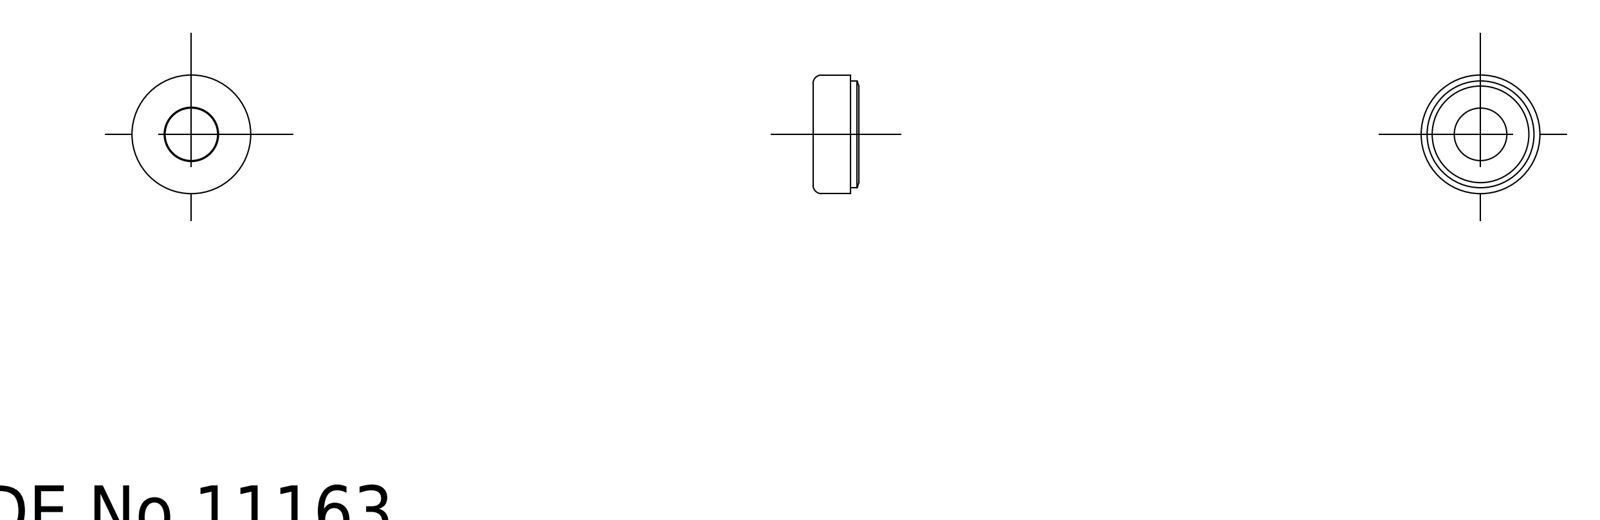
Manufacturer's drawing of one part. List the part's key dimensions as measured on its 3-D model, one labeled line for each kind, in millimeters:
Part name (STEP PRODUCT): washer; packing; TL_421_M3
STEP written by: SolidWorks 2015 (AUTOMOTIVE_DESIGN)
Units: millimetres
Bodies: 2 solids, 22 faces (6 planar, 12 cylindrical, 4 other)
Overall size (bounding box): 7 × 7 × 2.7
Volume: 78 mm³ · Surface area: 250 mm²
Round holes (diameter × count): ⌀3.1 ×1, ⌀3.2 ×1, ⌀6 ×1
Round bosses / shafts (diameter × count): ⌀7 ×1, ⌀6.3 ×1
Main face-to-face distances: 0.5, 2.2, 2.7, 1.7
